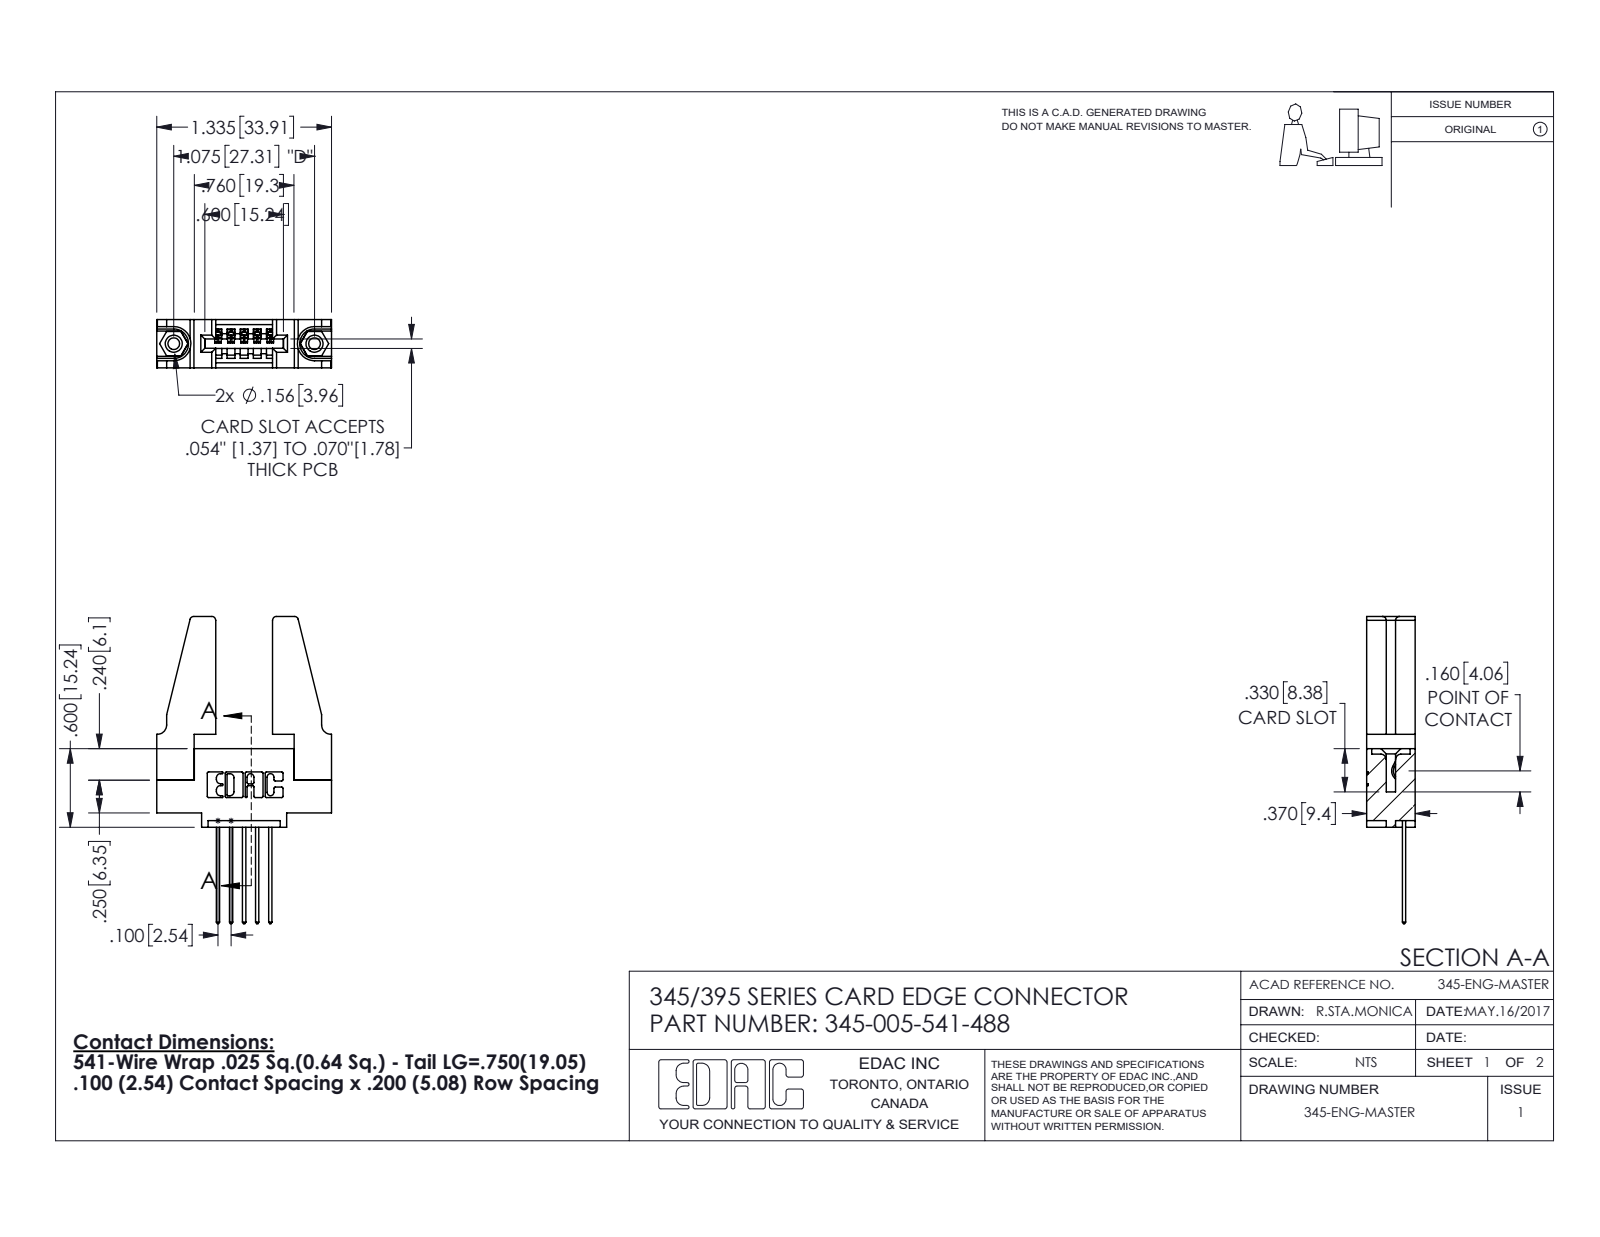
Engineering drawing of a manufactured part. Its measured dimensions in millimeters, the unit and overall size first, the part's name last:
Units: millimetres
Overall size (bounding box): 59.6 × 33.9 × 9.4
Round holes (diameter × count): ⌀2.3 ×2, ⌀3.2 ×2, ⌀4 ×2, ⌀1.6 ×1
Round bosses / shafts (diameter × count): ⌀3.9 ×2
Partial cylindrical surfaces — rounded edges, fillets, slot ends (radius × count): R0.3 ×22, R0.2 ×10, R0.3 ×10, R0.8 ×8, R0.2 ×6, R0.8 ×6, R0.7 ×3, R0.8 ×2
Main face-to-face distances: 9.4, 1.8, 7.6, 5.1, 3.8, 3.8, 2.5, 6.9, 0.6, 5.6
Hole centre spacings: 6.9, 21.5, 27.3
Volume: 6 110 mm³ · Surface area: 6 613 mm²
Bodies: 10 solids, 544 faces (356 planar, 172 cylindrical, 16 other)
Part name (STEP PRODUCT): 345-220-078_345-220-088; 345-005-541-488; 345 Part_0.110 Offset - 0.156 Dia-TH; 345-292-001_345-293-141 (+1 more)
STEP written by: SolidWorks 2016 (CONFIG_CONTROL_DESIGN)
